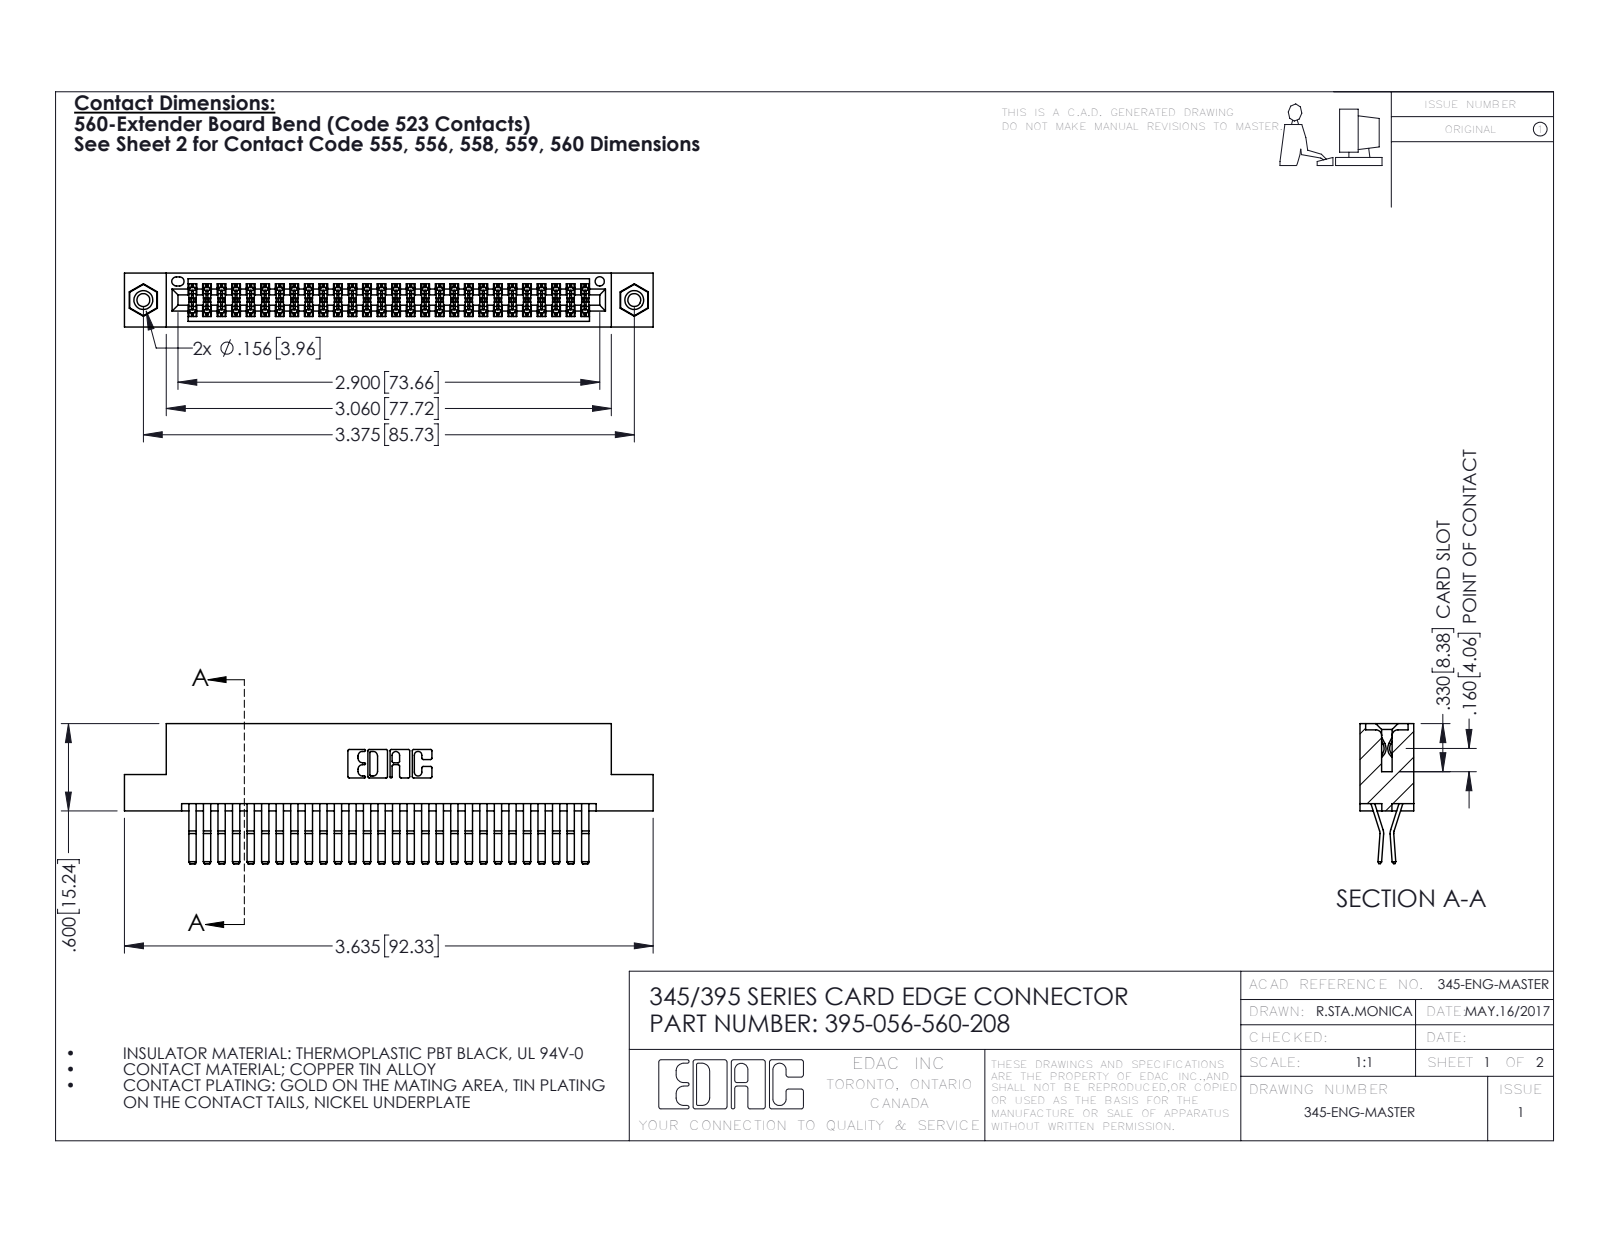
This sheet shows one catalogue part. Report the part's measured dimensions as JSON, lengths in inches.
{"part_name": "345 Part_Flush Mounting Lugs - 0.156 Dia-TI; 345-250-001_345-250-003-102; 395-056-560-208; 345-292-001_560 Tail", "step_written_by": "SolidWorks 2016 (CONFIG_CONTROL_DESIGN)", "units": "inches", "bodies": {"solids": 59, "faces": 3098, "planar": 1960, "cylindrical": 1122, "other": 16}, "overall_size": [3.635, 0.962, 0.37], "volume_in3": 0.561, "surface_area_in2": 22.14, "round_holes": [[0.089, 2], [0.125, 2], [0.156, 2], [0.064, 1]], "round_bosses_or_shafts": [[0.155, 2]], "partial_cylinders_radius": [[0.006, 111], [0.01, 22], [0.007, 6], [0.031, 6], [0.026, 3], [0.01, 2], [0.014, 2], [0.019, 2]], "face_to_face_distances": [0.025, 0.072, 0.298, 0.2, 0.37, 0.098, 0.272, 0.225, 0.175, 0.149], "hole_center_spacings": [0.27, 3.14, 3.375]}
